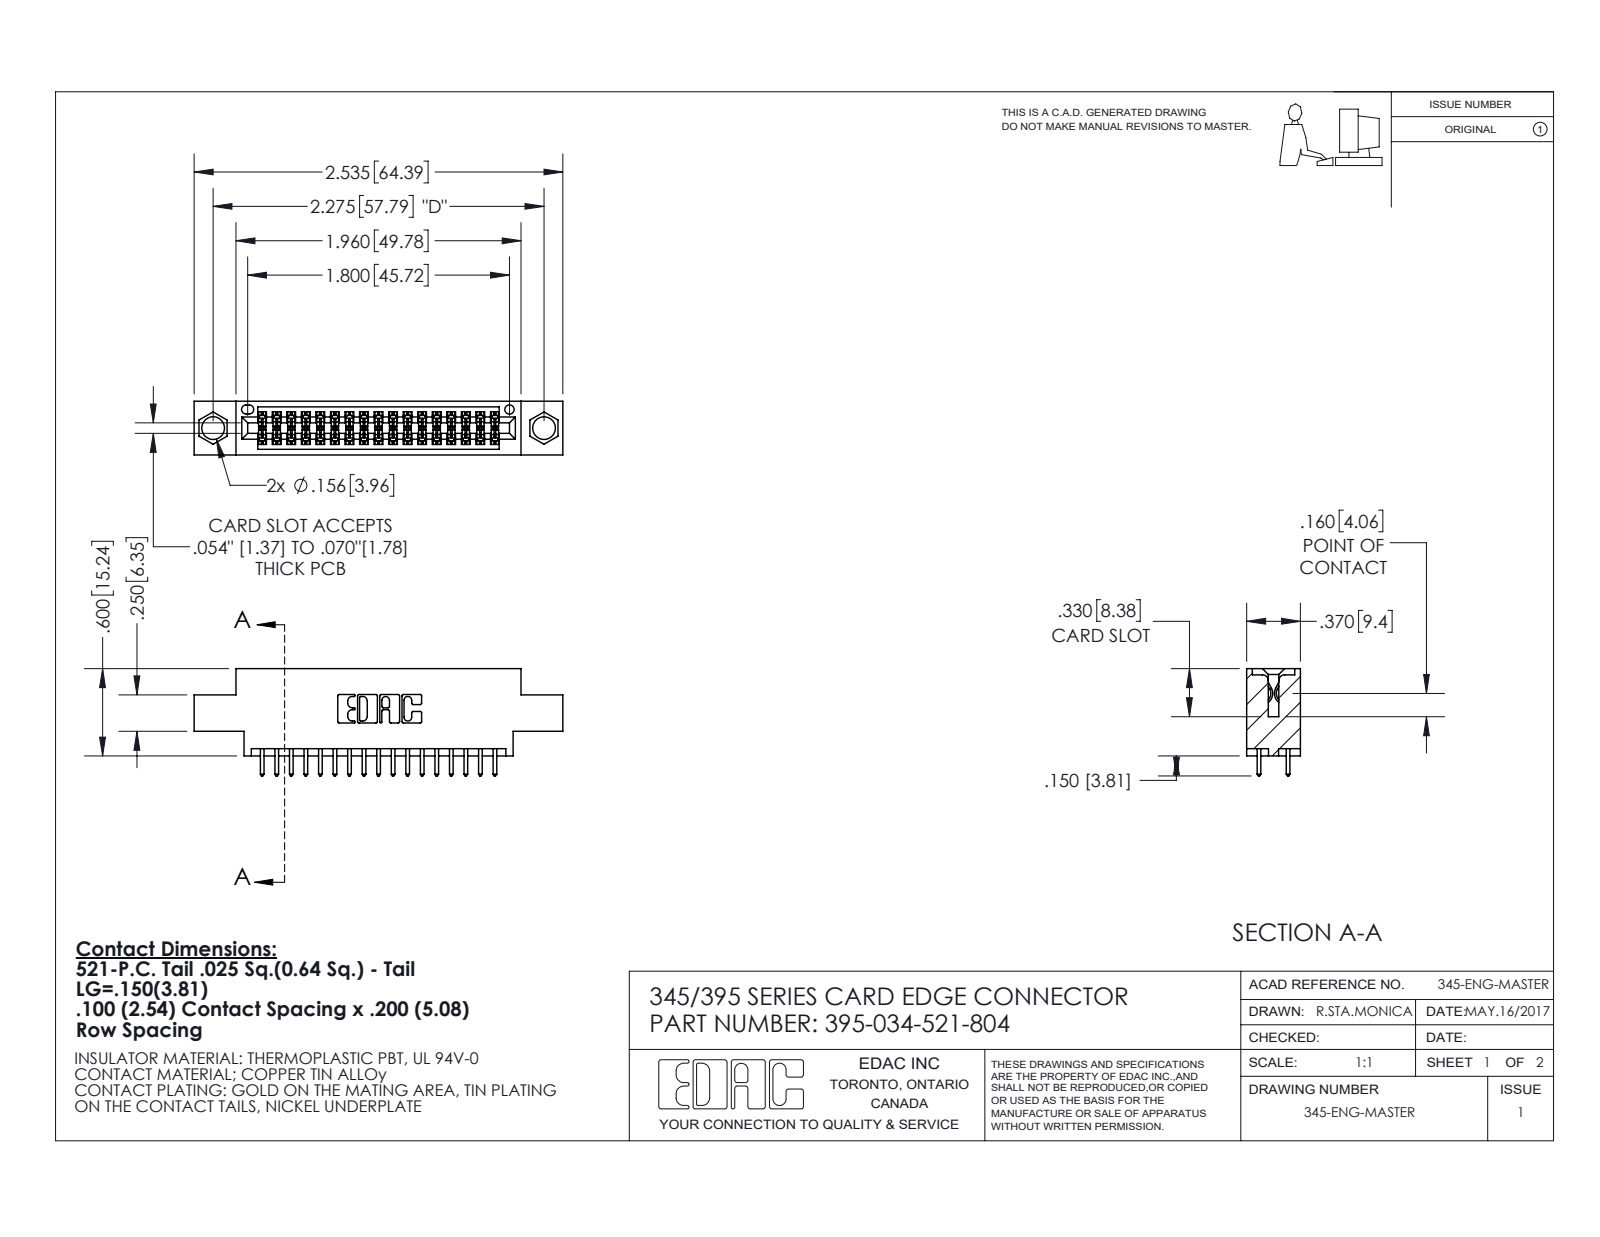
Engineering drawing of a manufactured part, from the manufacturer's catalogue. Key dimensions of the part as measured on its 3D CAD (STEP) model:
Part name (STEP PRODUCT): 345 Part_0.170 Offset - 0.156 Dia-TI; 345-292-001_345-293-121; 395-034-521-804
STEP written by: SolidWorks 2020 (CONFIG_CONTROL_DESIGN)
Units: inches
Bodies: 35 solids, 1844 faces (1220 planar, 624 cylindrical, 0 other)
Overall size (bounding box): 2.535 × 0.737 × 0.37
Volume: 0.353 in³ · Surface area: 12.37 in²
Round holes (diameter × count): ⌀0.156 ×2, ⌀0.064 ×1
Partial cylindrical surfaces — rounded edges, fillets, slot ends (radius × count): R0.006 ×51, R0.01 ×34, R0.01 ×22, R0.007 ×6, R0.031 ×6, R0.026 ×3, R0.014 ×2, R0.019 ×2
Main face-to-face distances: 0.072, 0.298, 0.2, 0.37, 0.098, 0.272, 0.025, 0.225, 0.175, 0.1
Hole centre spacings: 0.27, 2.041, 2.275
